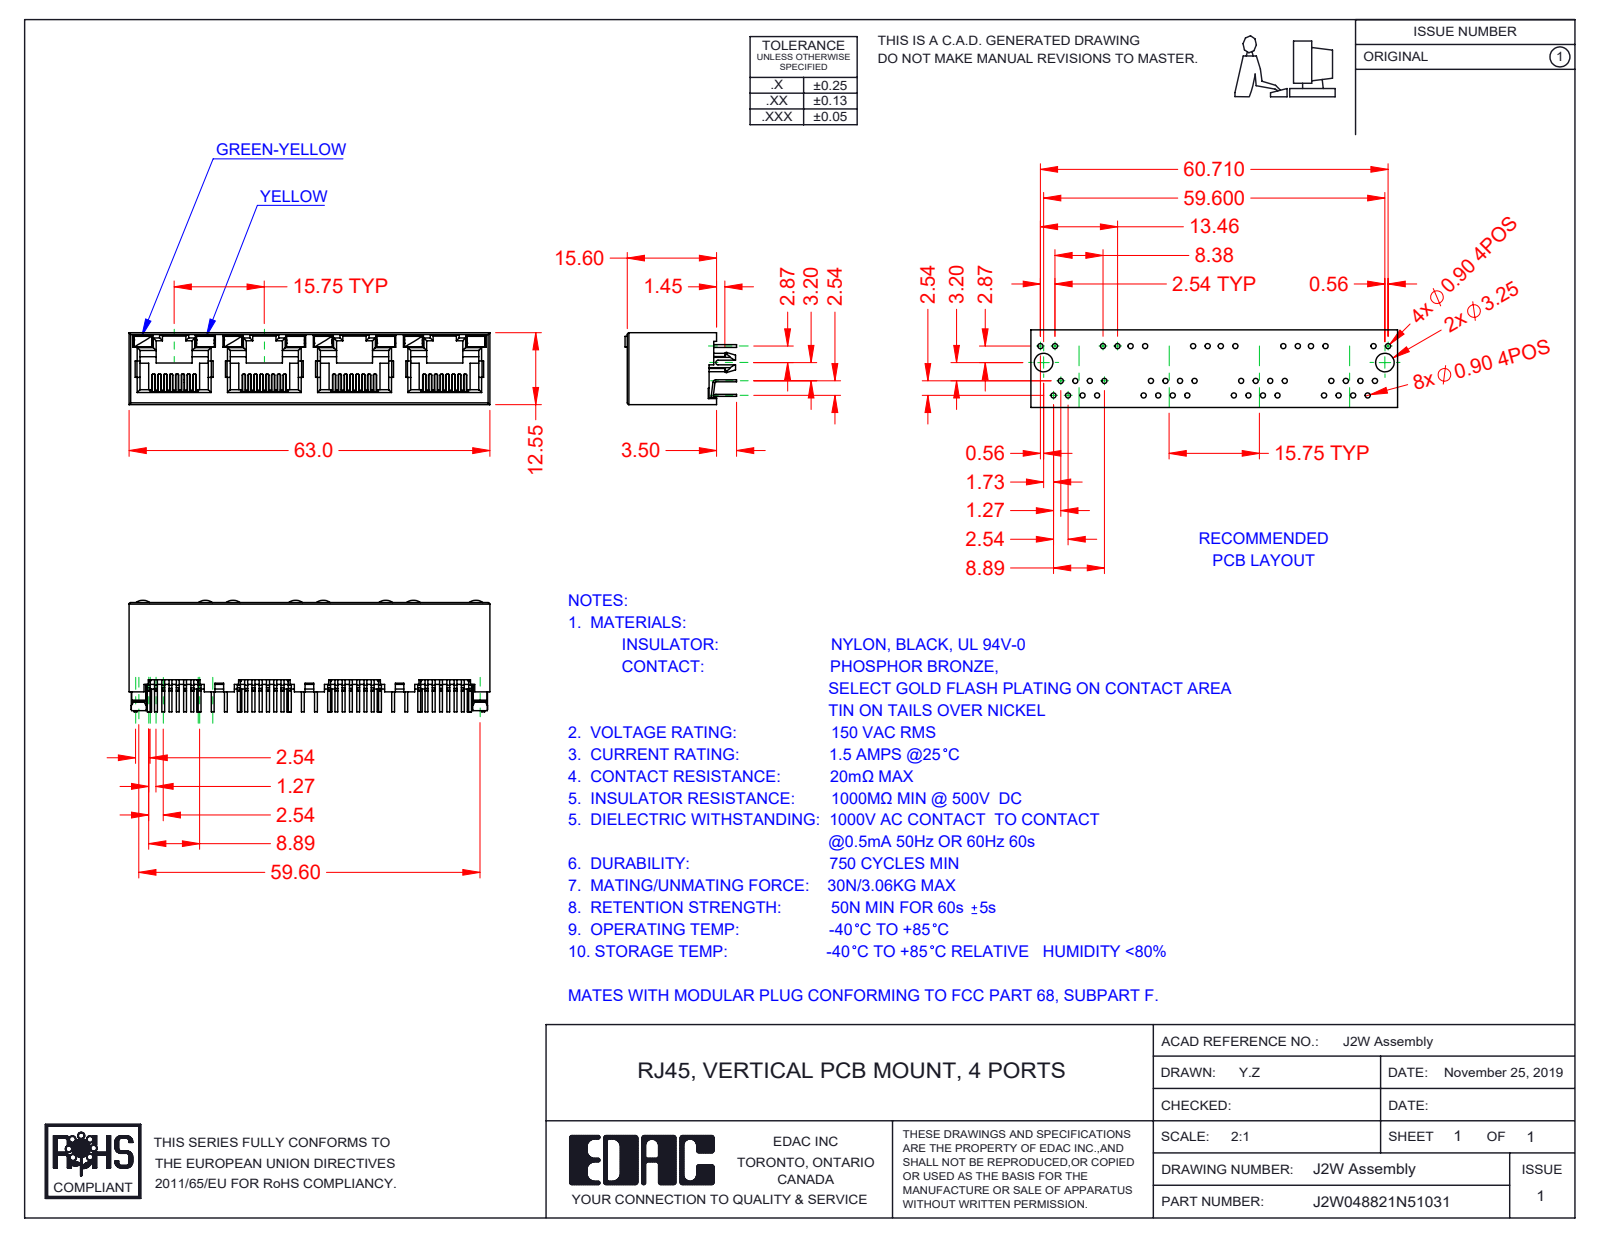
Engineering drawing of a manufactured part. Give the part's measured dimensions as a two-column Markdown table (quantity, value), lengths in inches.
| quantity | value |
| --- | --- |
| part name | 2W Contacts; J2W048821N51131; 2W LED RH_1-Yellow; 2W Insulator (+2 more) |
| STEP written by | SolidWorks 2016 (CONFIG_CONTROL_DESIGN) |
| units | inches |
| bodies | 45 solids, 3139 faces (2600 planar, 481 cylindrical, 58 other) |
| overall size | 2.48 × 0.768 × 0.494 |
| volume | 0.326 in³ |
| surface area | 20.37 in² |
| partial cylindrical surfaces (radius × count) | 0.006 × 64, 0.008 × 29, 0.02 × 28, 0.012 × 14, 0.018 × 8, 0.079 × 8, 0.01 × 2, 0.059 × 2 |
| main face-to-face distances | 0.494, 0.469, 0.026, 0.62, 0.014, 0.059, 0.031, 0.024, 0.445, 1.24 |
